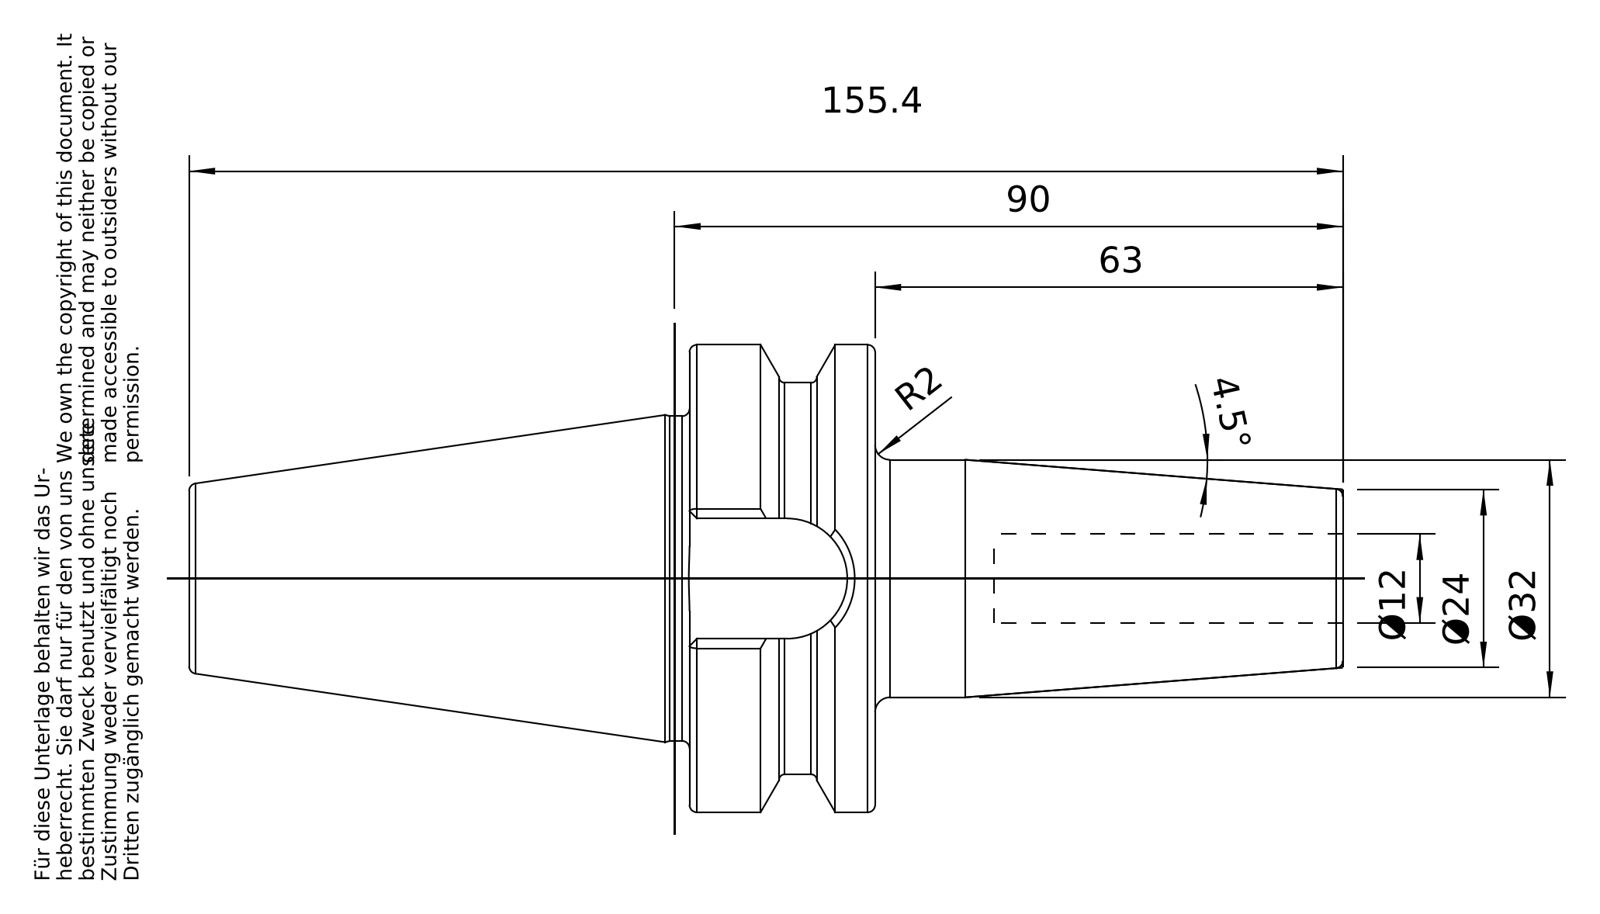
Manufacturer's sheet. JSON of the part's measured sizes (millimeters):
{"part_name": "40-640-12", "step_written_by": "PRO/ENGINEER BY PARAMETRIC TECHNOLOGY CORPORATION, 2010430 (CONFIG_CONTROL_DESIGN)", "units": "millimeters", "bodies": {"solids": 1, "faces": 96, "planar": 26, "cylindrical": 22, "other": 48}, "overall_size": [155.4, 62.98, 62.98], "volume_mm3": 162202, "surface_area_mm2": 28850, "round_holes": [[12, 1], [13.84, 1], [17.01, 1], [17.5, 1]], "round_bosses_or_shafts": [[62.98, 1], [52.75, 1], [43.75, 1], [32, 1], [16.01, 1]], "partial_cylinders_radius": [[8.1, 1]], "face_to_face_distances": [25, 44.9, 88, 63, 16.2, 67.4, 92.4, 155.4, 108.4, 41]}
